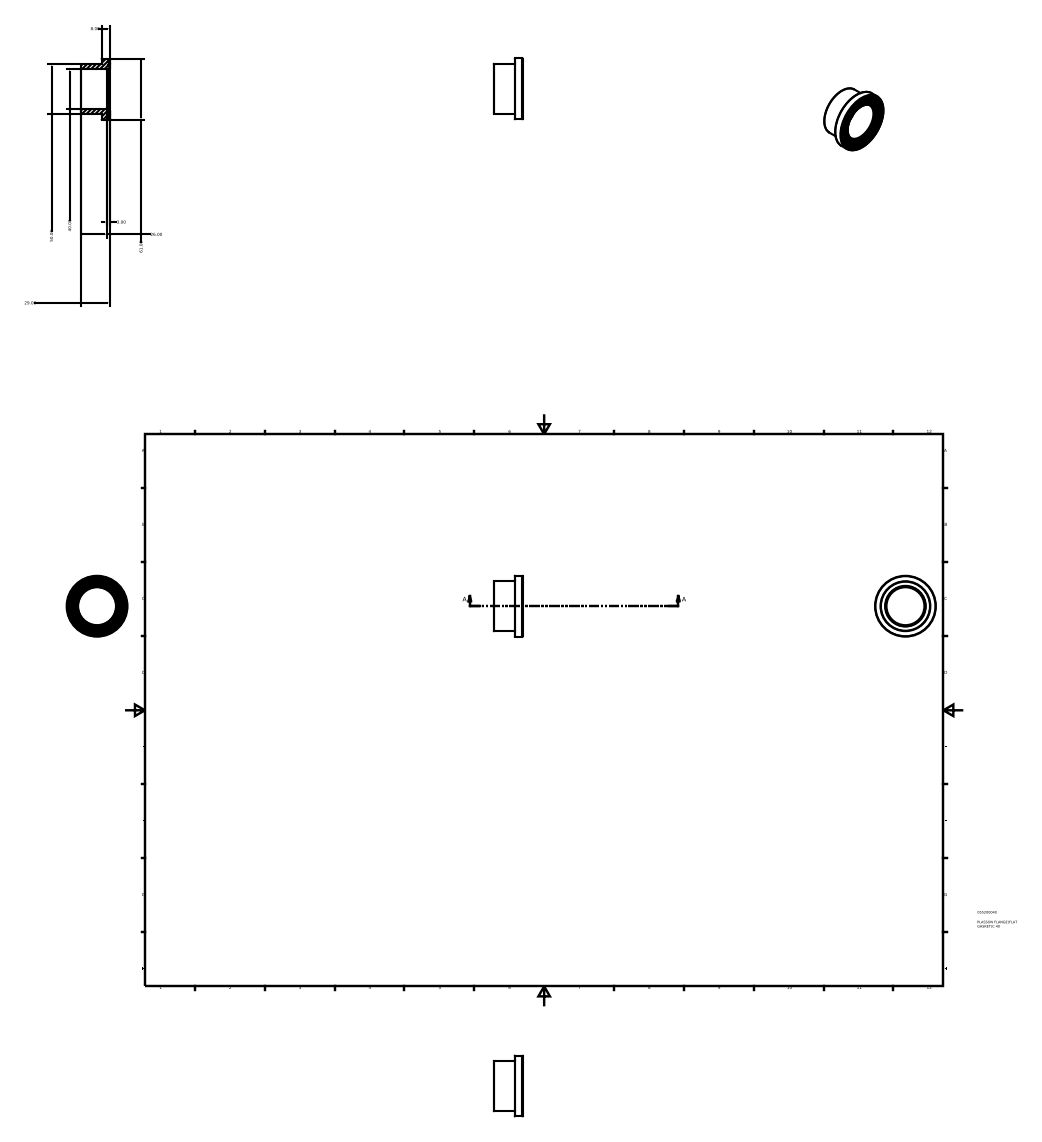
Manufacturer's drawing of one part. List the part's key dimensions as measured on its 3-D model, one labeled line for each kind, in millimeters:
Part name (STEP PRODUCT): 055200040
STEP written by: Autodesk Inventor 2015 (AUTOMOTIVE_DESIGN)
Units: millimetres
Bodies: 1 solid, 33 faces (9 planar, 9 cylindrical, 15 other)
Overall size (bounding box): 61 × 61 × 29
Volume: 27 480 mm³ · Surface area: 12 422 mm²
Round holes (diameter × count): ⌀38 ×1, ⌀40 ×1, ⌀41.83 ×1, ⌀49.5 ×1, ⌀57.17 ×1
Round bosses / shafts (diameter × count): ⌀61 ×1, ⌀53.33 ×1, ⌀50 ×1, ⌀45.67 ×1
Main face-to-face distances: 21, 29, 8, 27.8, 6.8, 1.2, 26, 5, 1.8, 3
